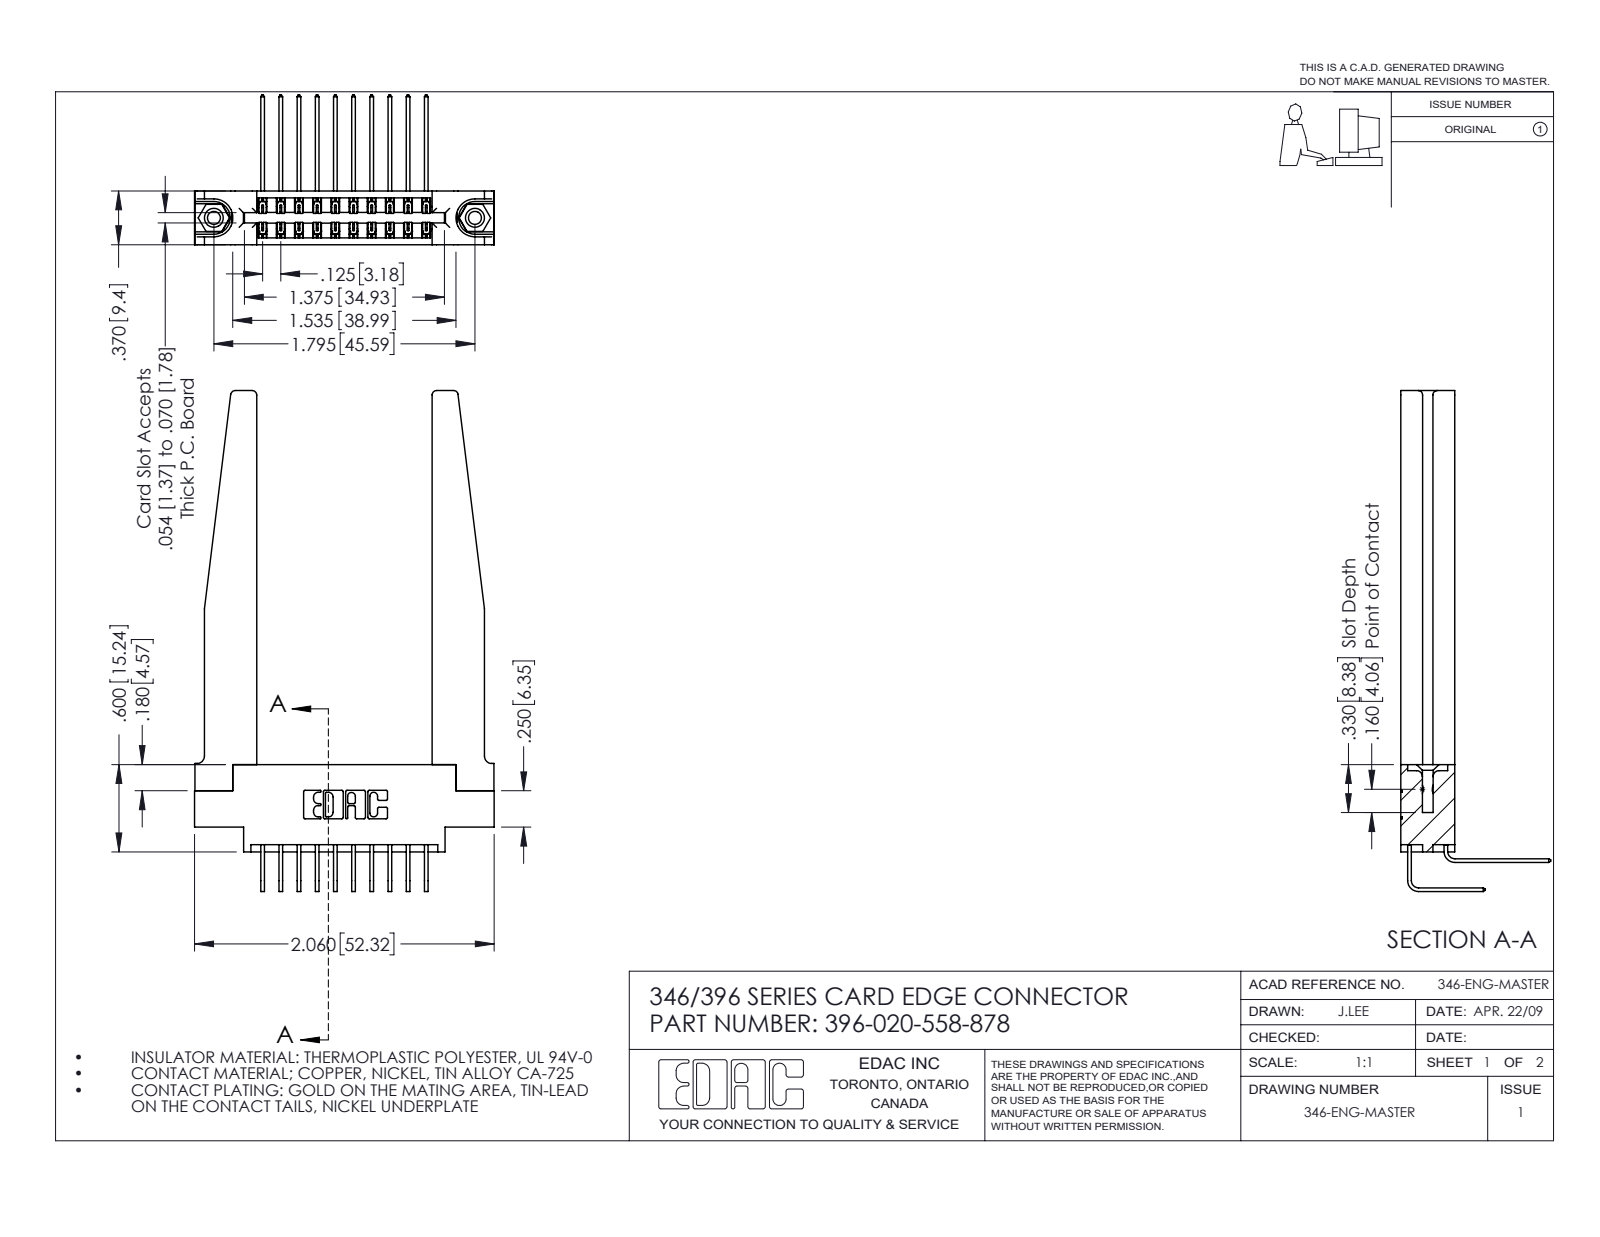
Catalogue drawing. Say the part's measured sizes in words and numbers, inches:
The part is named "346 Part_0.170 Offset - 0.156 Dia-TH; 345-250-001_345-250-001-102; 346-220-078_345-220-078; 396-020-558-878 (+2 more)". Its 3-D file was written by "SolidWorks 2016 (CONFIG_CONTROL_DESIGN)". It is 25 solids with 1440 faces: 962 planar, 426 cylindrical and 52 other. Overall it measures 3.443 by 2.06 by 1.03 inches. Its volume is 0.715 cubic inches and its surface area 20.75 square inches. Round holes: 2 of diameter 0.089, 2 of diameter 0.125, 2 of diameter 0.156, 1 of diameter 0.064. Round bosses or shafts: 2 of diameter 0.155. Partial cylindrical surfaces (rounded edges, fillets, slot ends): 30 of radius 0.006, 22 of radius 0.01, 8 of radius 0.03, 6 of radius 0.007, 6 of radius 0.031, 4 of radius 0.05, 3 of radius 0.026, 2 of radius 0.014. The main face-to-face distances are 0.37, 0.15, 0.072, 0.048, 0.322, 0.148, 0.25, 0.22, 0.102, 0.173. The hole center spacings are 0.246, 1.59, 1.795.
